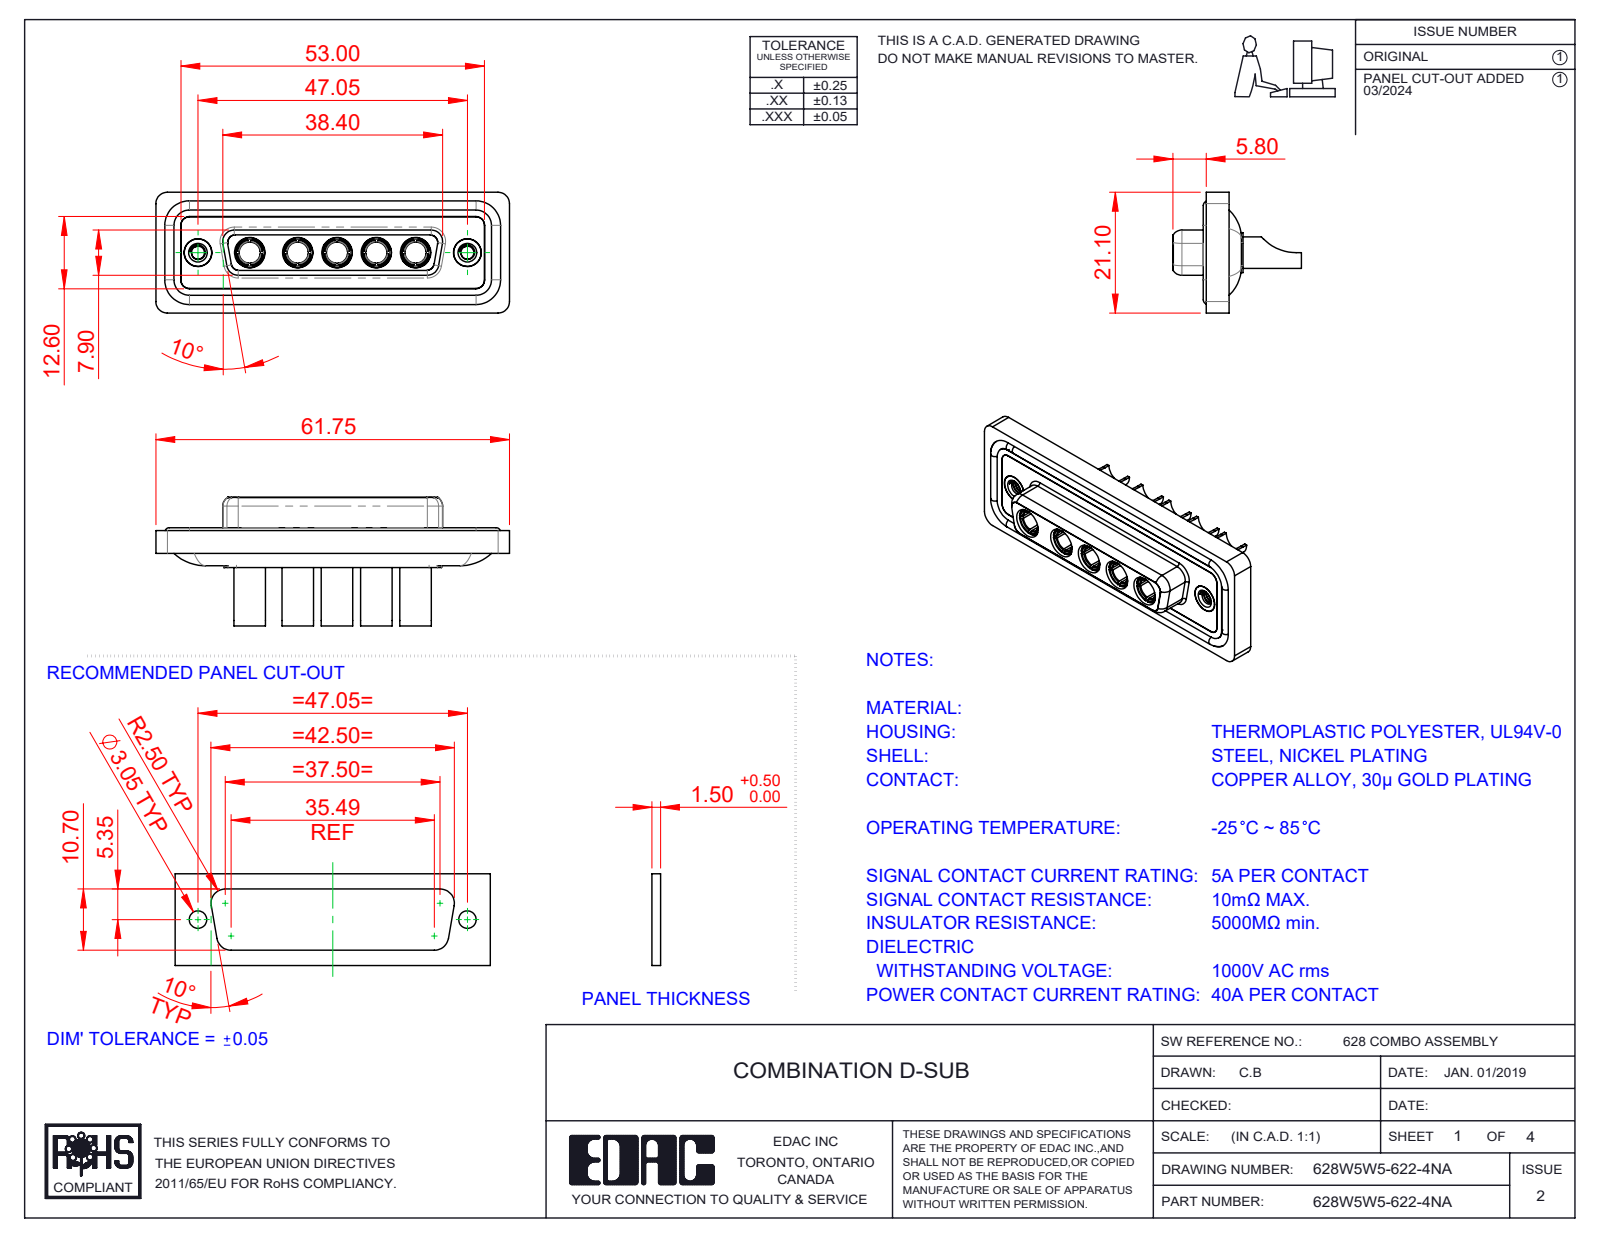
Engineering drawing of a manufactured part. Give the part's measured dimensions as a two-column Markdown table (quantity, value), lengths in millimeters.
| quantity | value |
| --- | --- |
| part name | 628Combo Waterproof Housing_25 Contacts; 628W5W5-622-4NA; 628Combo Housing_5W5; Power Socket_40A SC (+3 more) |
| STEP written by | SolidWorks 2023 (CONFIG_CONTROL_DESIGN) |
| units | millimeters |
| bodies | 17 solids, 769 faces (260 planar, 310 cylindrical, 199 other) |
| overall size | 61.75 × 22.45 × 21.1 |
| volume | 8 374 mm³ |
| surface area | 14 112 mm² |
| round holes (diameter × count) | 4.85 × 7, 3.7 × 5, 4.6 × 5, 5.3 × 5, 2.26 × 2, 4 × 2, 4.05 × 2, 5 × 2 |
| round bosses / shafts (diameter × count) | 5.5 × 5, 5.2 × 5, 4.96 × 5, 4.75 × 5, 3.75 × 5, 1.6 × 4, 4.95 × 2, 4.8 × 2 |
| partial cylindrical surfaces (radius × count) | 1.5 × 22, 2 × 18, 1.35 × 8, 1.6 × 8, 2.1 × 5, 0.25 × 4, 0.5 × 4, 0.6 × 4 |
| main face-to-face distances | 0.4, 7.45, 1.8, 5.65, 0.5, 7.05, 6.6, 1.6, 1.1, 2.9 |
| hole center spacings | 6.86, 9.04, 13.72, 38.01, 8.39, 15.25, 15.9, 17.43 |
